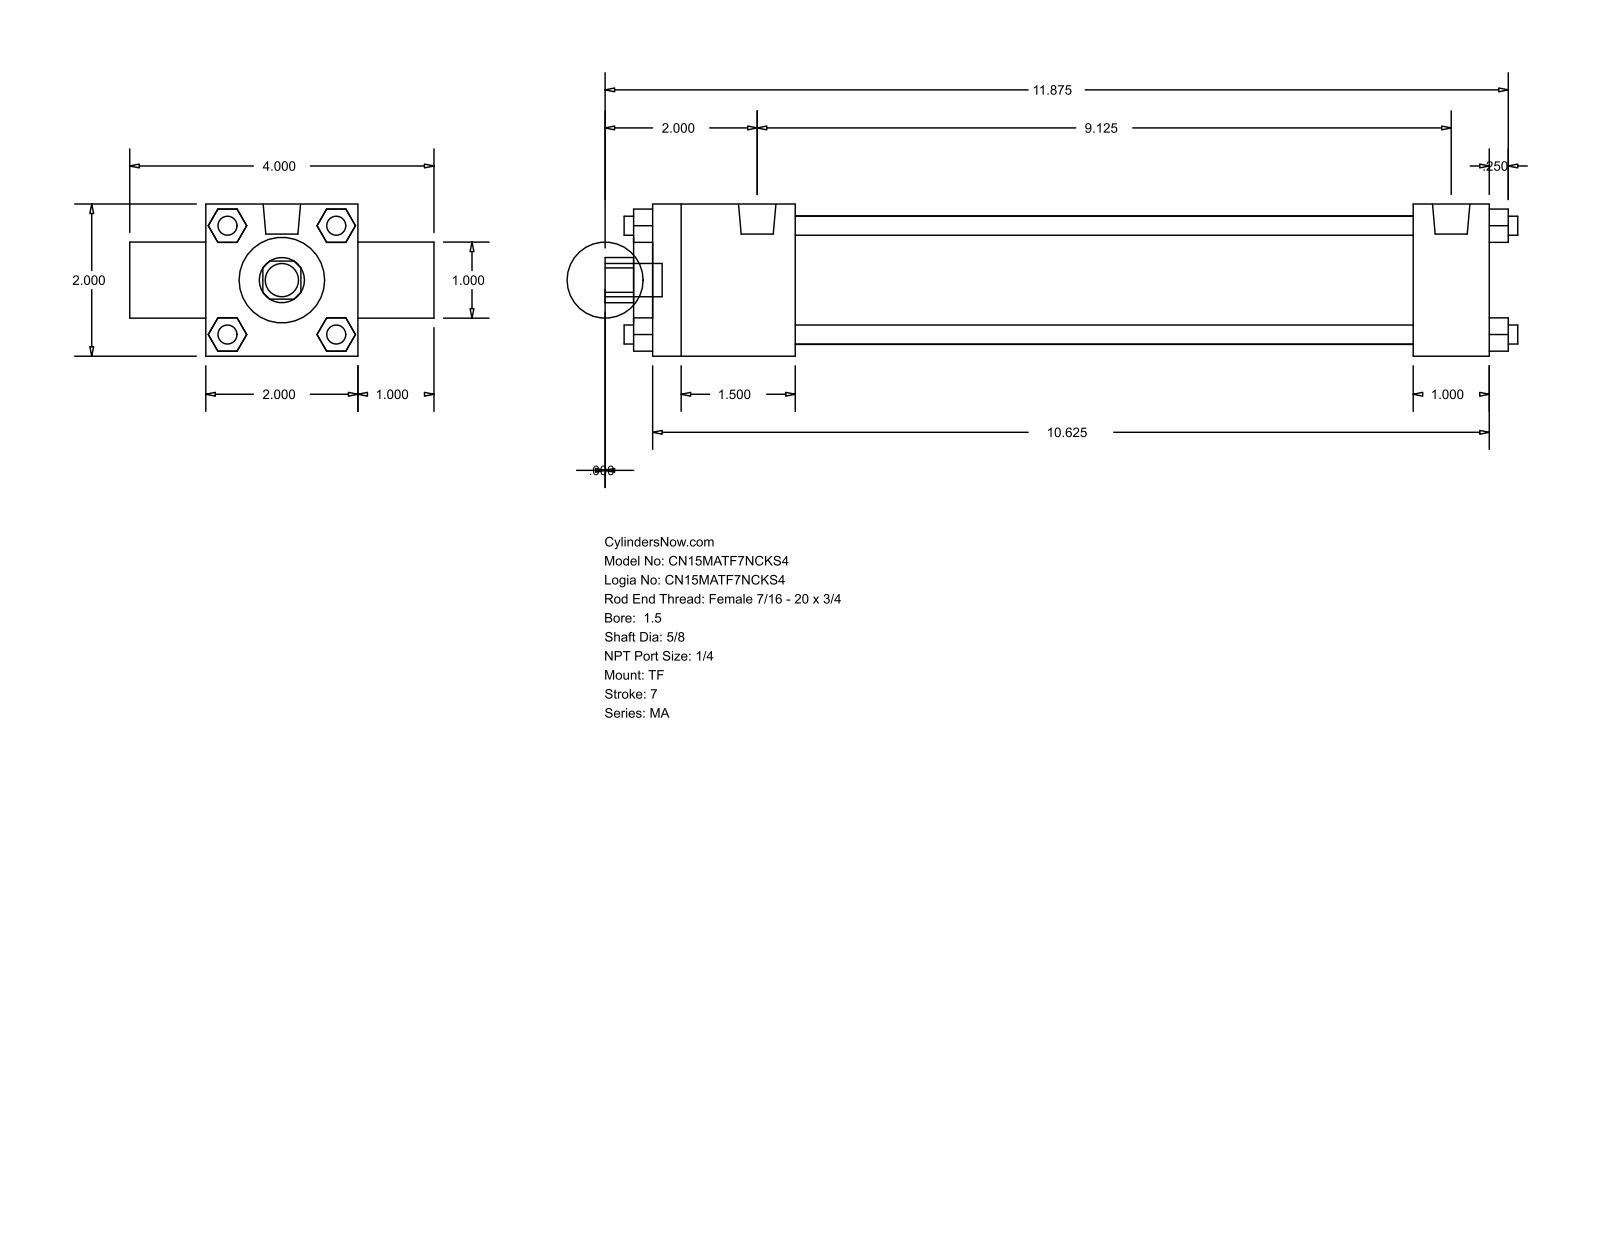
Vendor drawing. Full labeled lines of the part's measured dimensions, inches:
Part name (STEP PRODUCT): MA_TF__0150_0.625
STEP written by: GSSL Pune (CONFIG_CONTROL_DESIGN)
Units: inches
Bodies: 0 solids, 120 faces (92 planar, 28 cylindrical, 0 other)
Overall size (bounding box): 12 × 4 × 2
Round holes (diameter × count): ⌀0.625 ×1, ⌀1 ×1, ⌀1.125 ×1, ⌀1.69 ×1
Round bosses / shafts (diameter × count): ⌀0.25 ×4, ⌀0.313 ×3, ⌀0.492 ×2, ⌀0.437 ×1
Partial cylindrical surfaces — rounded edges, fillets, slot ends (radius × count): R0.297 ×1
Main face-to-face distances: 2, 11, 0.25, 11.25, 1, 3, 1.875, 10, 8.125, 9.125
